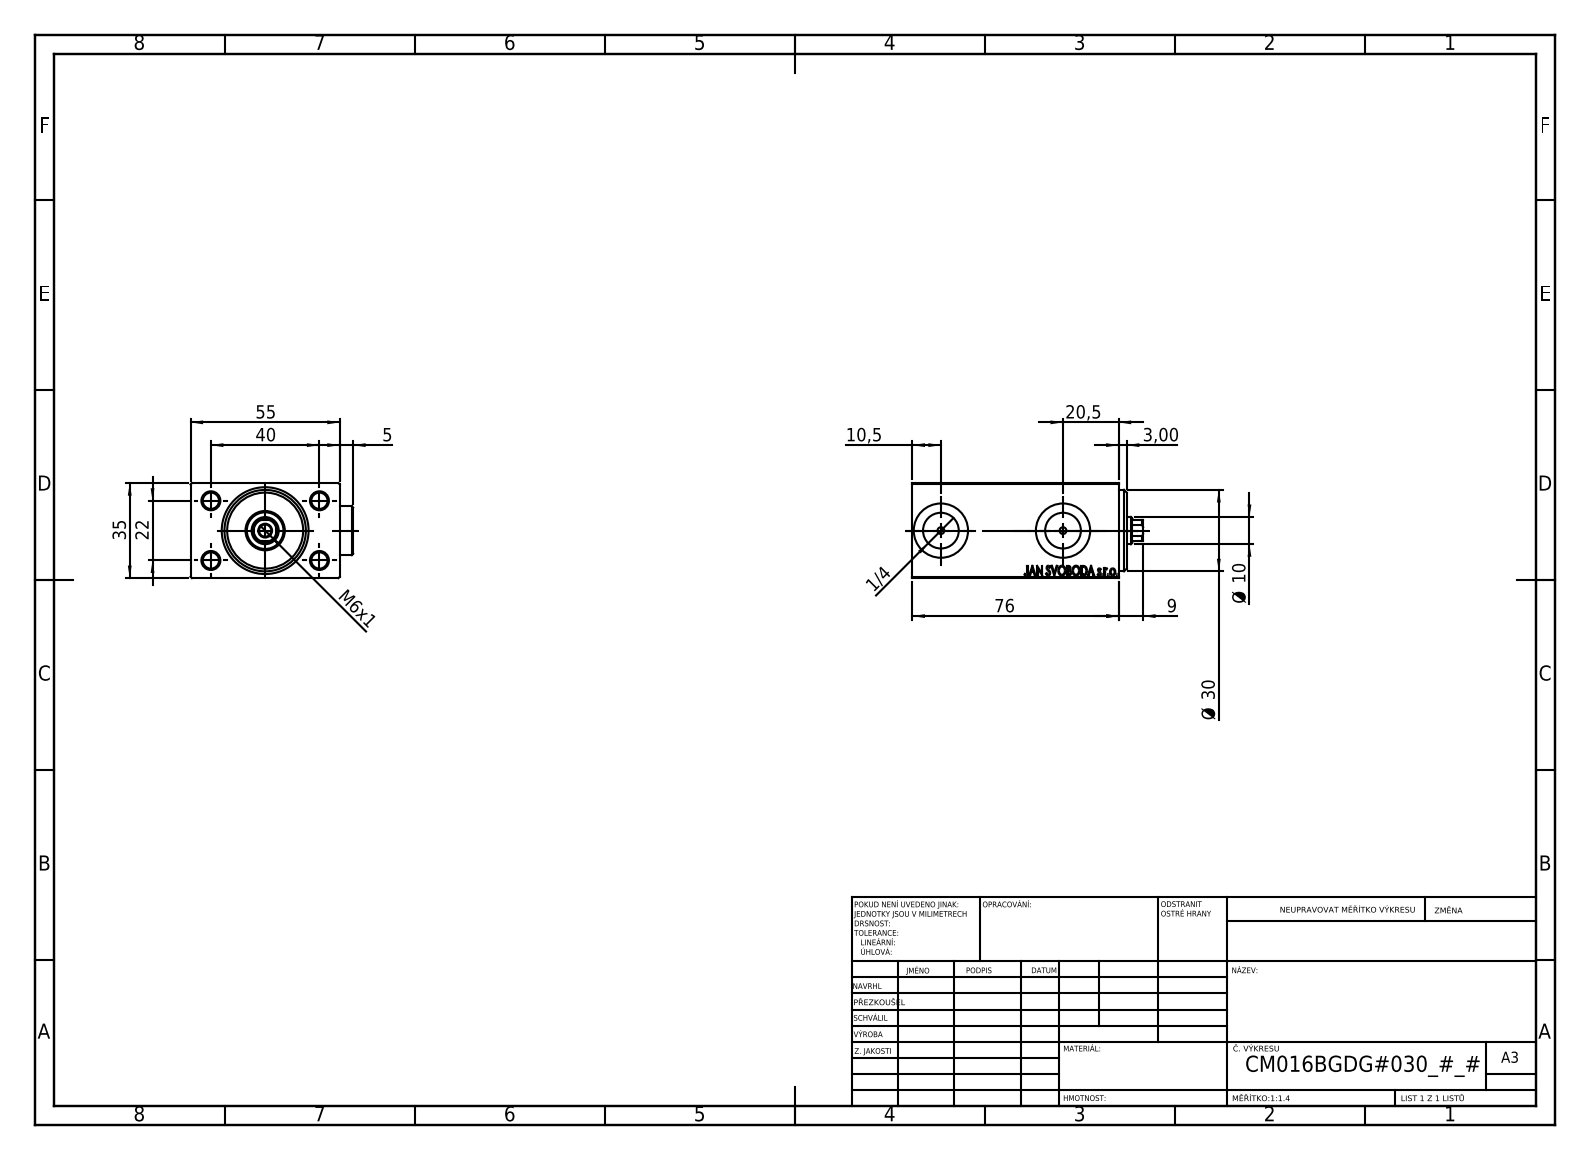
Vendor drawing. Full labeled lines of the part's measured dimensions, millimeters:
Part name (STEP PRODUCT): V450CM_VC_B; V450CM_B_Body; Zatka_OIL_PORT; V450CM_B_VCP
STEP written by: SolidWorks 2019 (CONFIG_CONTROL_DESIGN)
Units: millimetres
Bodies: 5 solids, 935 faces (435 planar, 70 cylindrical, 430 other)
Overall size (bounding box): 85 × 59.9 × 35
Volume: 137 265 mm³ · Surface area: 33 083 mm²
Round holes (diameter × count): ⌀6 ×4, ⌀2.5 ×2, ⌀13.16 ×2, ⌀20 ×2, ⌀4.5 ×1, ⌀10 ×1, ⌀13.5 ×1, ⌀14.5 ×1, ⌀16 ×1, ⌀18 ×1, ⌀30 ×1
Round bosses / shafts (diameter × count): ⌀18 ×2
Partial cylindrical surfaces — rounded edges, fillets, slot ends (radius × count): R4.5 ×1
Main face-to-face distances: 35, 55, 5, 71, 54.9, 76, 3, 8, 79, 54.8
Hole centre spacings: 22.83, 22, 40, 45.65, 45
